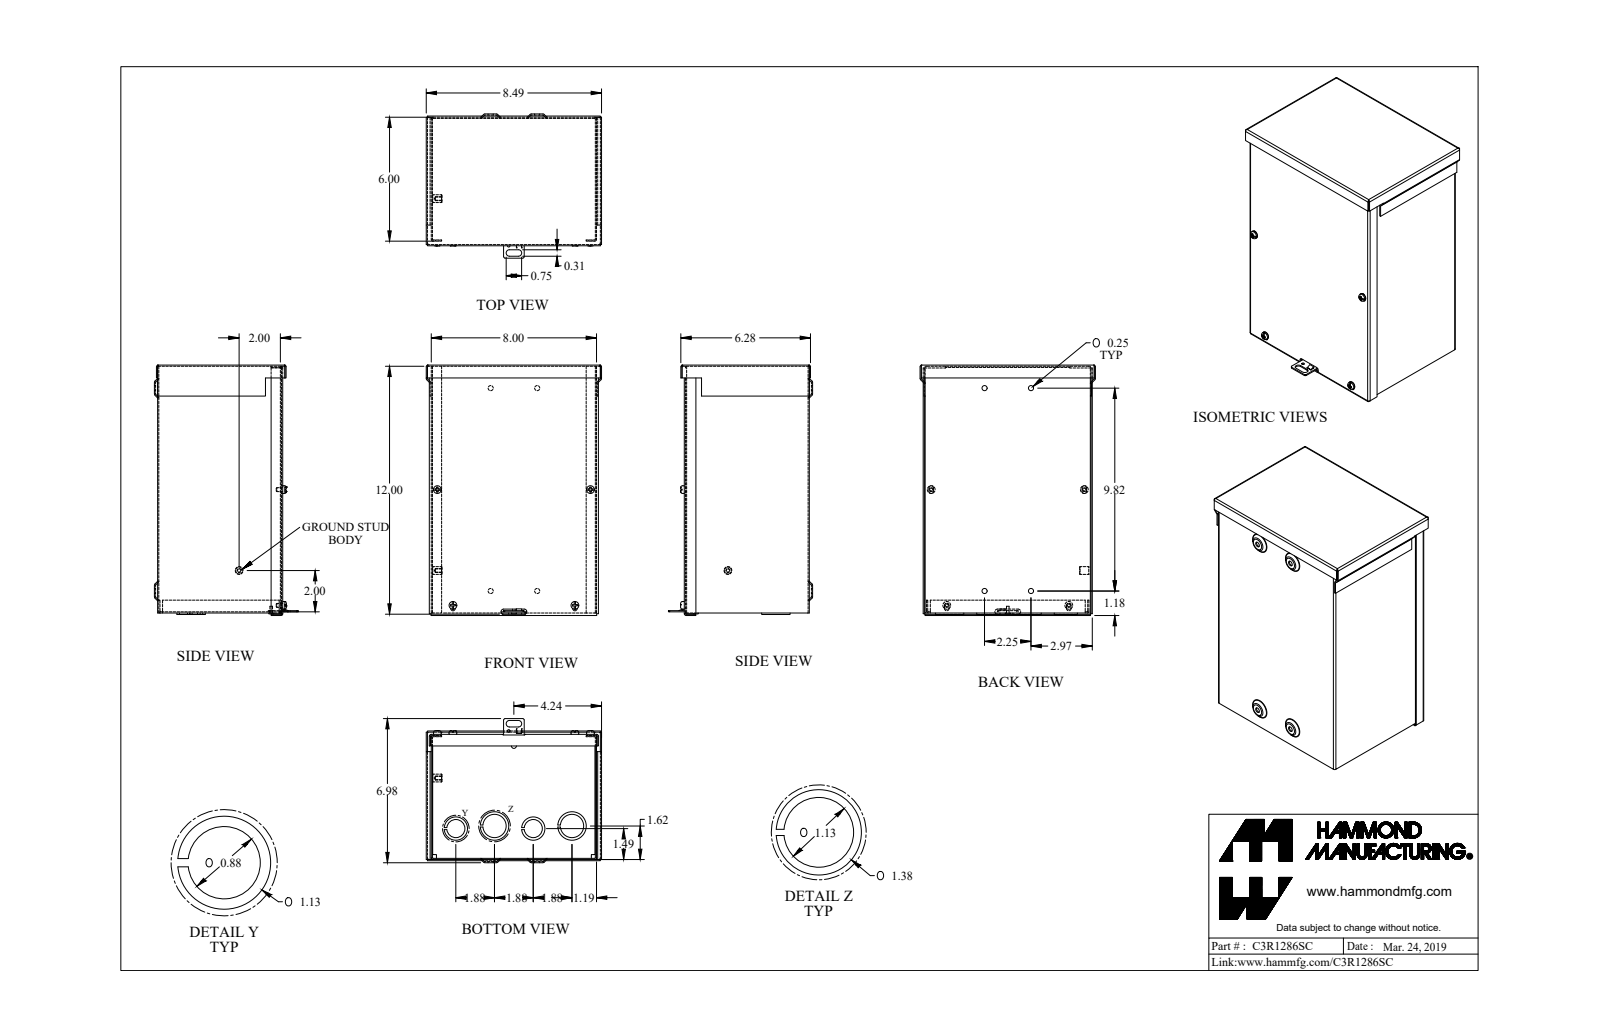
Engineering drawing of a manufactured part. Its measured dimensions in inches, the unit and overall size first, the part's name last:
Units: inches
Overall size (bounding box): 12.12 × 8.489 × 6.977
Round holes (diameter × count): ⌀0.17 ×4, ⌀0.25 ×4, ⌀0.125 ×1, ⌀0.137 ×1, ⌀0.156 ×1, ⌀0.875 ×1, ⌀0.875 ×1, ⌀1.125 ×1, ⌀1.125 ×1
Round bosses / shafts (diameter × count): ⌀0.375 ×4, ⌀0.19 ×4, ⌀1.125 ×2, ⌀1.375 ×1, ⌀1.375 ×1, ⌀0.375 ×1, ⌀0.125 ×1
Partial cylindrical surfaces — rounded edges, fillets, slot ends (radius × count): R0.029 ×21, R0.086 ×21, R0.109 ×8, R0.125 ×8, R0.156 ×2
Main face-to-face distances: 0.057, 6, 7.943, 5.943, 6.057, 8, 0.057, 7.886, 11.886, 11.943
Hole centre spacings: 5.547, 6.888, 1.88, 1.998, 2.25, 3.75, 4.165, 5.726
Volume: 28.91 in³ · Surface area: 1 022 in²
Bodies: 11 solids, 424 faces (223 planar, 115 cylindrical, 86 other)
Part name (STEP PRODUCT): C3R1286SC_Default
STEP written by: SolidWorks 2019 (CONFIG_CONTROL_DESIGN)
